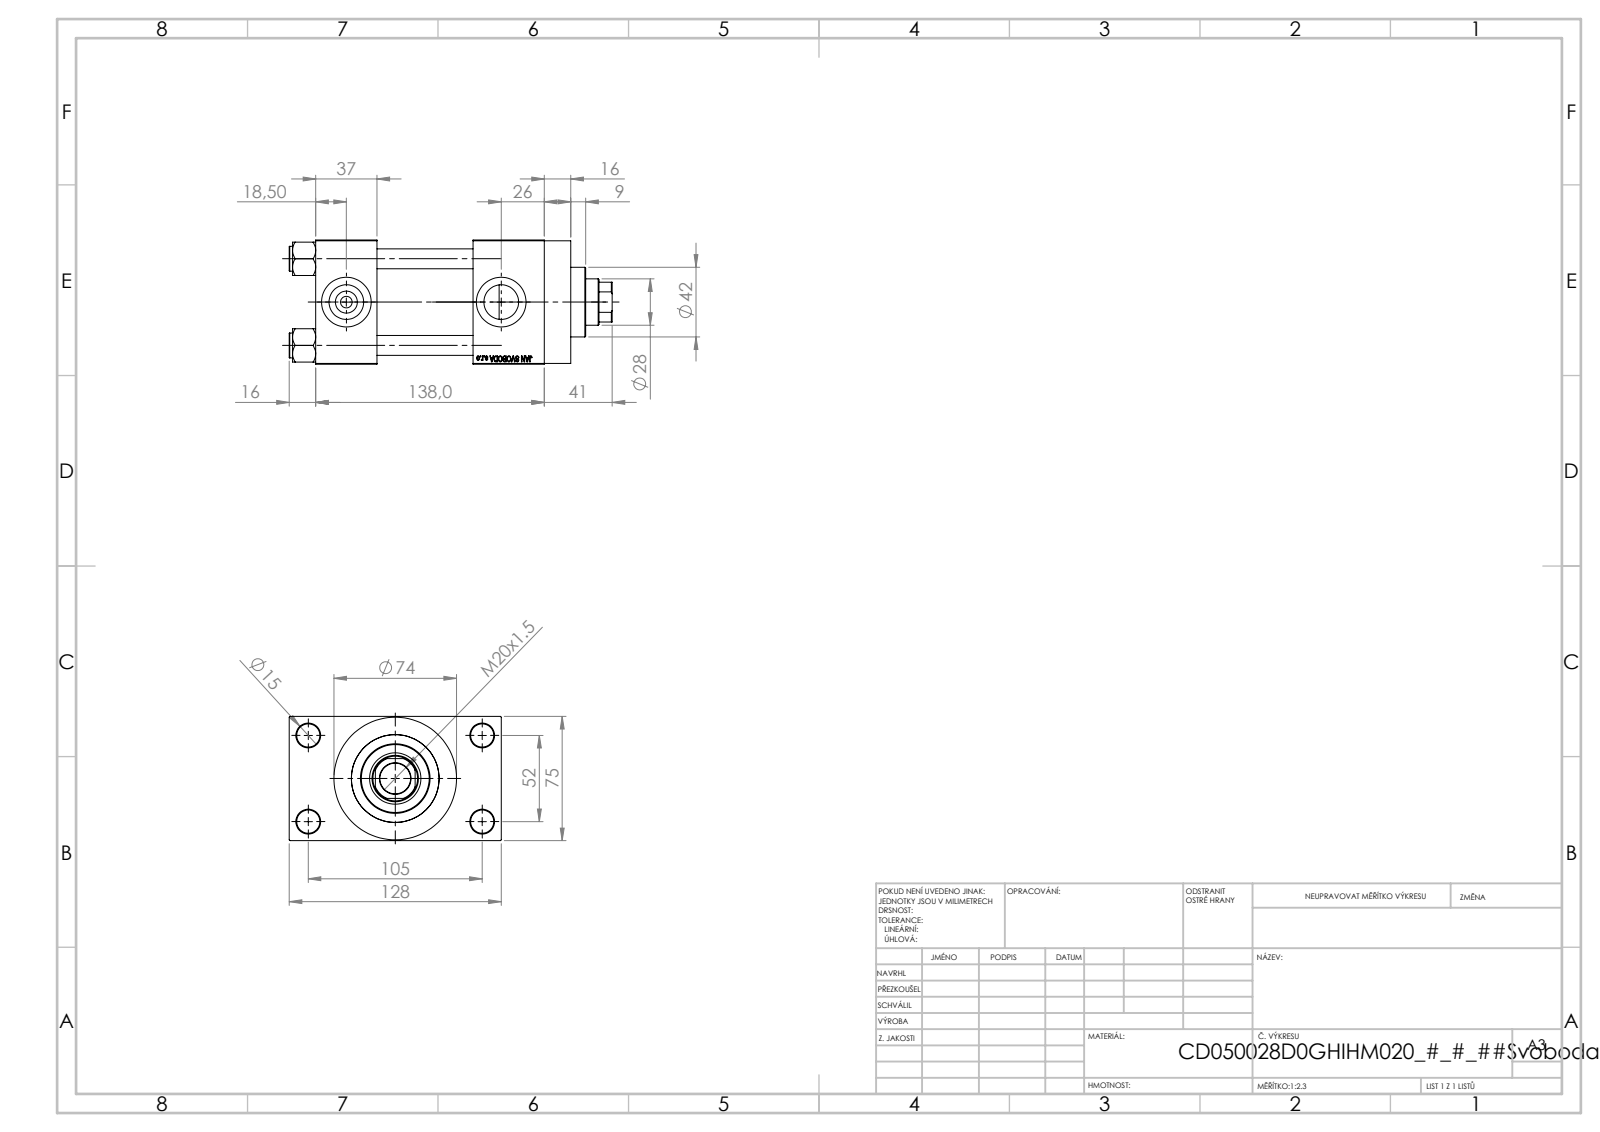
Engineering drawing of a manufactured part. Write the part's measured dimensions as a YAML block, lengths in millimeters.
part_name: "V215CD_NUT_M5_D; V215CD_D_TYCINKA; V215CD_VCP_D; V215CD_VC_A (+1 more)"
step_written_by: "SolidWorks 2019 (CONFIG_CONTROL_DESIGN)"
units: millimeters
bodies: {solids: 11, faces: 1103, planar: 497, cylindrical: 88, other: 518}
overall_size: [195, 128, 75]
volume: 806210
surface_area: 170608
round_holes:
  - {diameter: 12, count: 4}
  - {diameter: 14, count: 4}
  - {diameter: 7, count: 2}
  - {diameter: 20.96, count: 2}
  - {diameter: 30, count: 2}
  - {diameter: 18.5, count: 1}
  - {diameter: 28, count: 1}
  - {diameter: 31, count: 1}
  - {diameter: 41, count: 1}
  - {diameter: 50, count: 1}
  - {diameter: 53, count: 1}
round_bosses_or_shafts:
  - {diameter: 15, count: 4}
  - {diameter: 74, count: 1}
  - {diameter: 56, count: 1}
  - {diameter: 42, count: 1}
partial_cylinders:
  - {radius: 13.5, count: 1}
face_to_face_distances: [75, 58, 37, 95, 26.5, 138, 101, 43, 101.5, 16]
hole_center_spacings: [26.35, 36.98, 52.3, 58.43, 58.59, 78.65, 94.37, 52]
